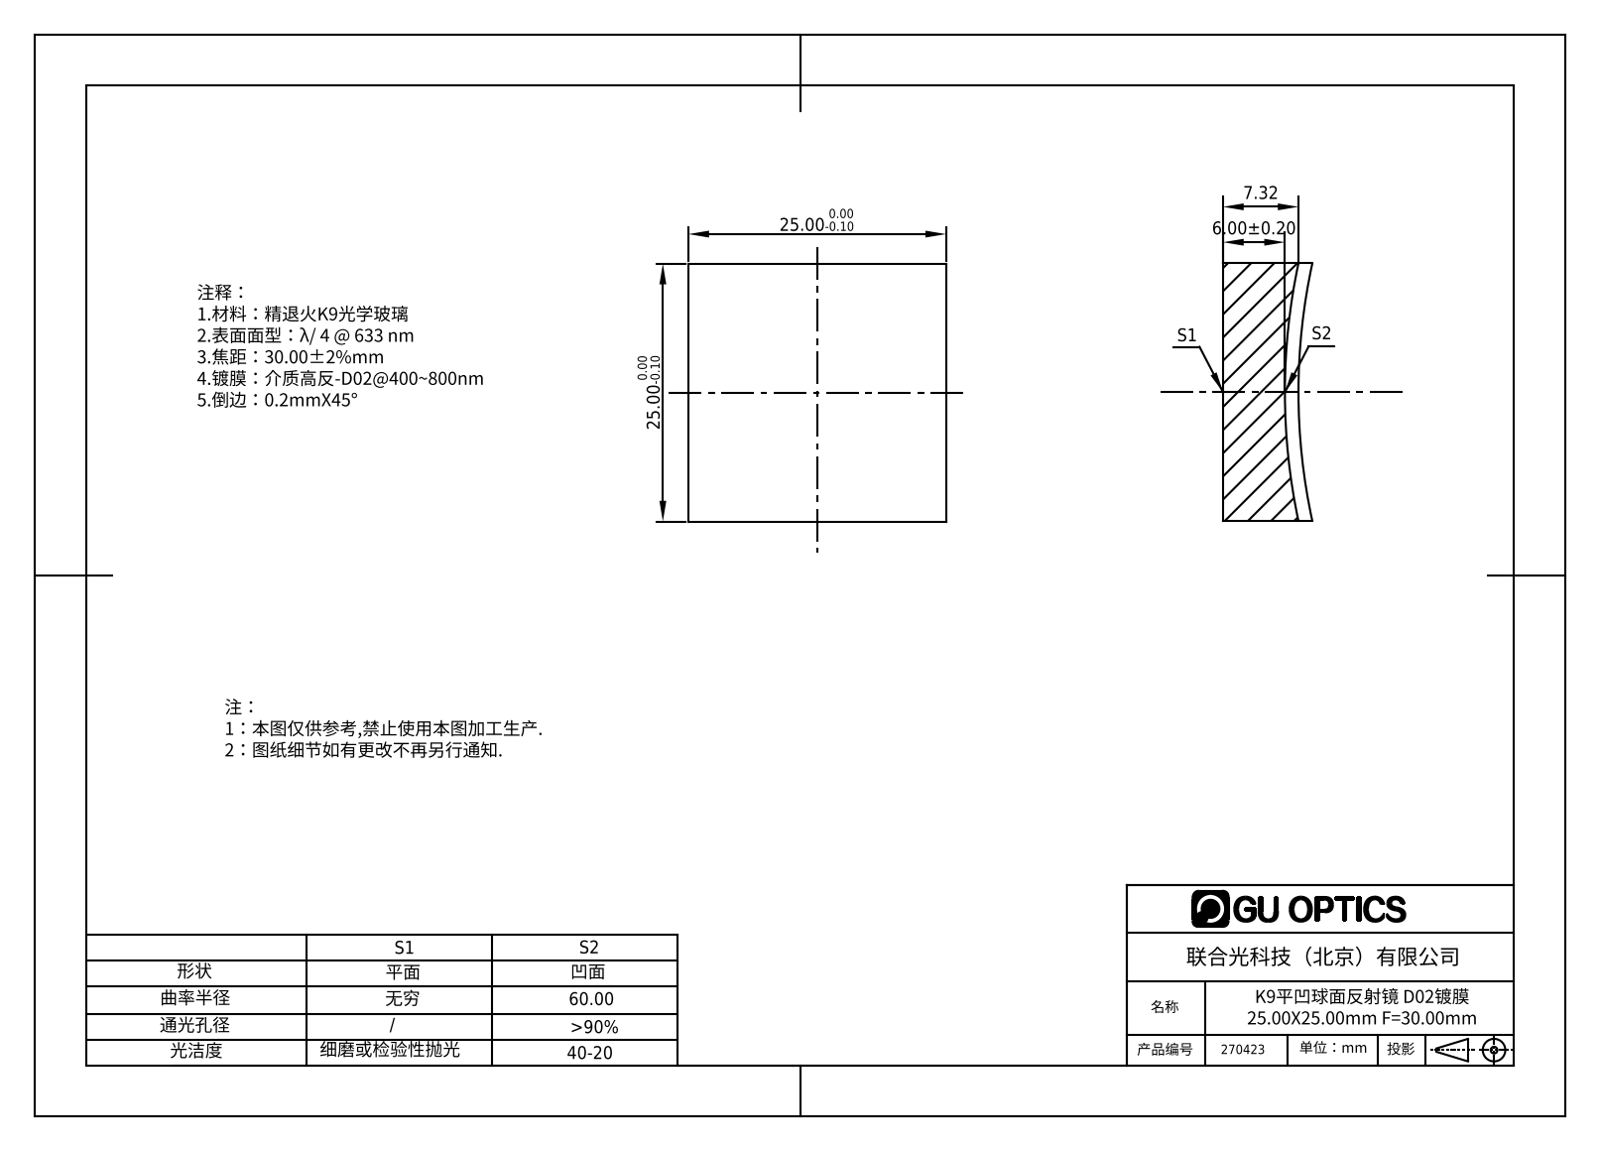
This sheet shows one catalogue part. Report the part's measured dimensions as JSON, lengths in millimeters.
{"part_name": "270033", "step_written_by": "SolidWorks 2019 (AUTOMOTIVE_DESIGN)", "units": "millimeters", "bodies": {"solids": 1, "faces": 7, "planar": 5, "cylindrical": 0, "other": 2}, "overall_size": [25, 25, 8.66], "volume_mm3": 4298, "surface_area_mm2": 2036, "face_to_face_distances": [25]}
